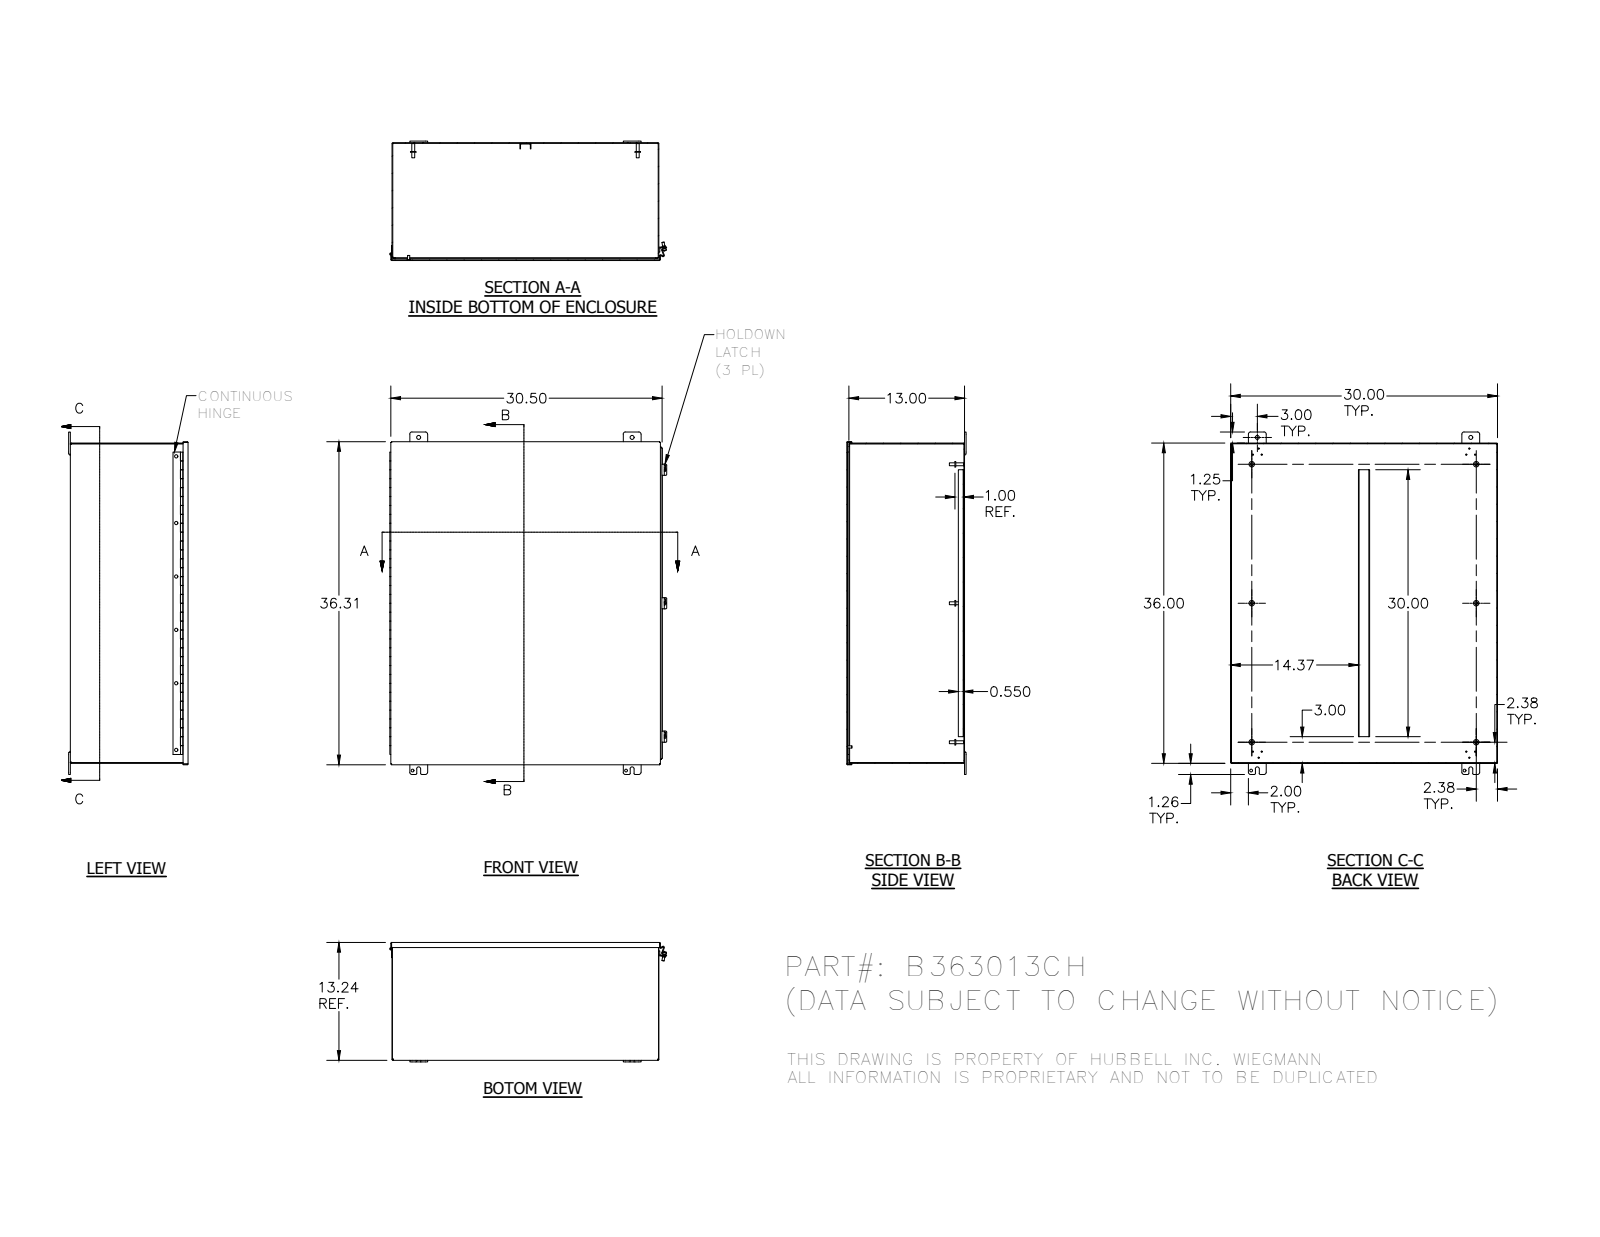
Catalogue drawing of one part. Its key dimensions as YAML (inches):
part_name: "B363013CH; B363013CHBKP; B3630CHLID; H6010103 (+8 more)"
step_written_by: "Autodesk Inventor 2012 (AUTOMOTIVE_DESIGN)"
units: inches
bodies: {solids: 26, faces: 852, planar: 529, cylindrical: 245, other: 78}
overall_size: [38.505, 31.136, 13.423]
volume: 309.6
surface_area: 8375
round_holes:
  - {diameter: 0.11, count: 6}
  - {diameter: 0.375, count: 6}
  - {diameter: 0.313, count: 4}
  - {diameter: 0.438, count: 4}
  - {diameter: 0.196, count: 3}
  - {diameter: 0.125, count: 1}
  - {diameter: 0.125, count: 1}
round_bosses_or_shafts:
  - {diameter: 0.625, count: 6}
  - {diameter: 0.33, count: 6}
  - {diameter: 0.25, count: 5}
  - {diameter: 0.41, count: 3}
  - {diameter: 0.344, count: 3}
  - {diameter: 0.337, count: 1}
  - {diameter: 0.12, count: 1}
partial_cylinders:
  - {radius: 0.125, count: 20}
  - {radius: 0.25, count: 16}
  - {radius: 0.063, count: 12}
  - {radius: 0.031, count: 8}
  - {radius: 0.07, count: 8}
  - {radius: 0.105, count: 8}
  - {radius: 0.063, count: 7}
  - {radius: 0.133, count: 6}
face_to_face_distances: [0.074, 13.169, 13.095, 13.243, 29.926, 35.926, 30, 29.852, 36, 35.852]
hole_center_spacings: [15, 24, 0.75, 1.593, 6, 36.005, 43.271, 1.134]
